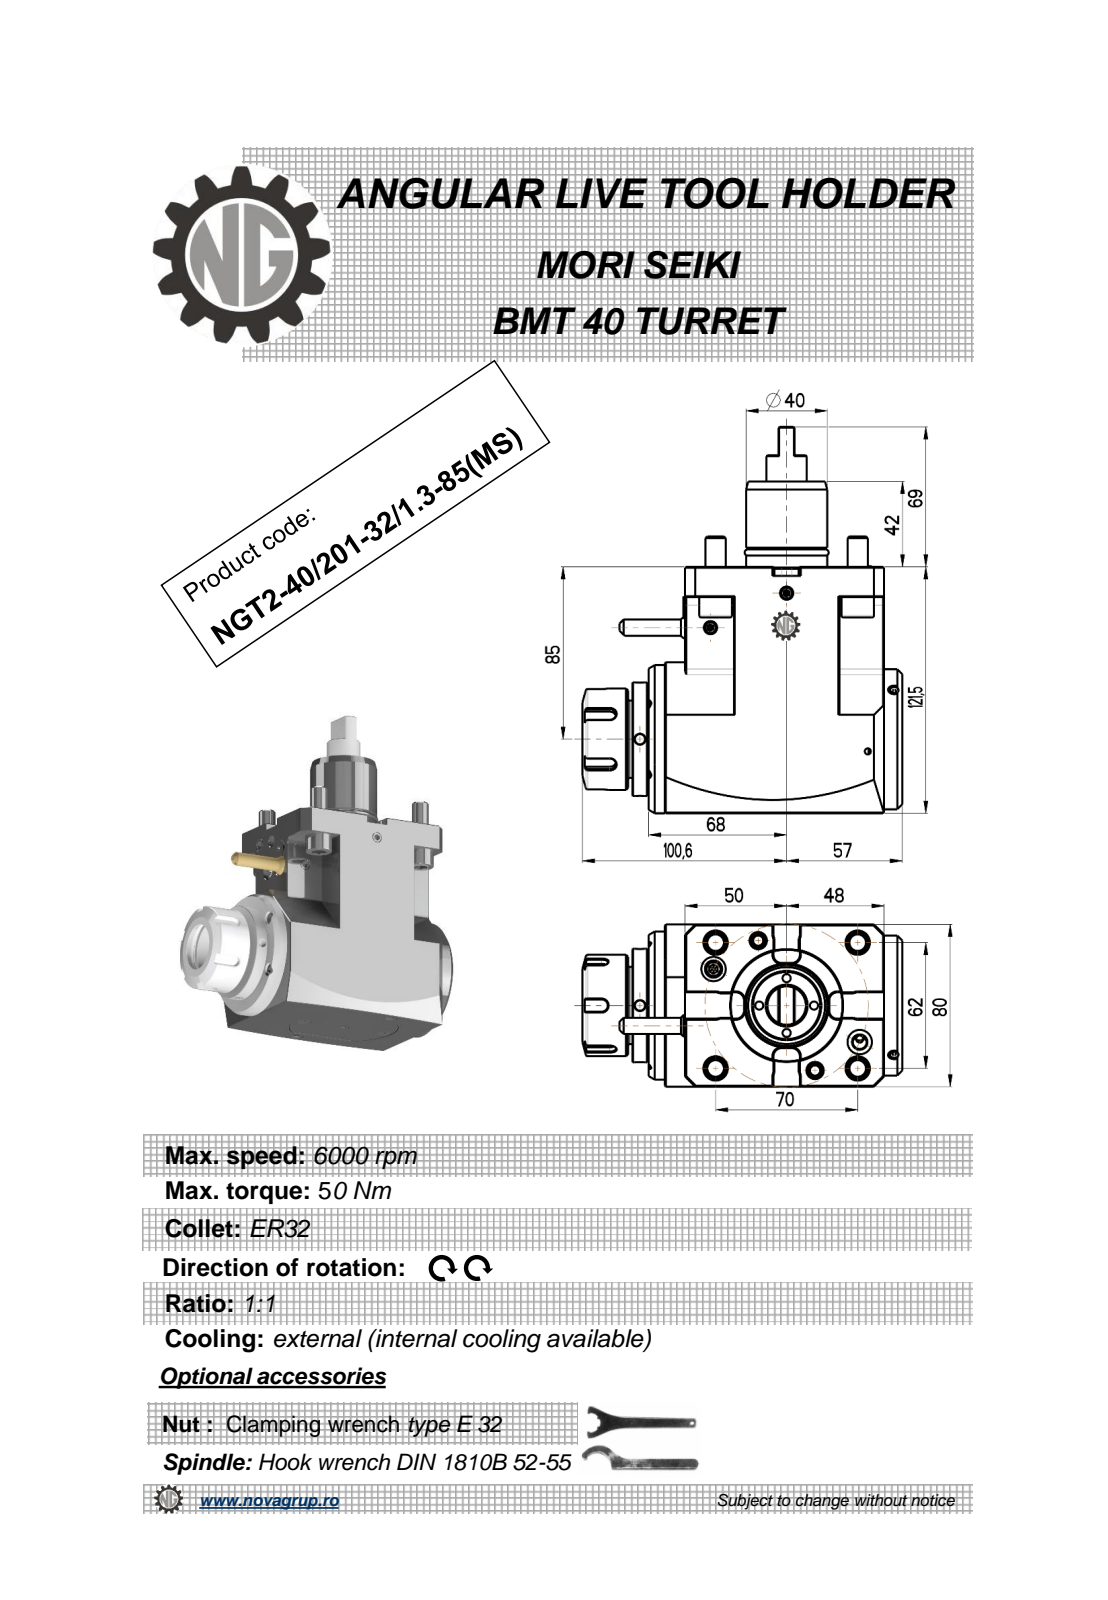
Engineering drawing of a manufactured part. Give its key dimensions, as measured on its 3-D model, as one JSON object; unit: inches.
{"part_name": "NGT2_40_201_32_1_3_85_MS", "step_written_by": "PRO/ENGINEER BY PARAMETRIC TECHNOLOGY CORPORATION, 2010280 (CONFIG_CONTROL_DESIGN)", "units": "inches", "bodies": {"solids": 2, "faces": 484, "planar": 179, "cylindrical": 105, "other": 200}, "overall_size": [7.5, 6.205, 3.213], "volume_in3": 66.45, "surface_area_in2": 145.2, "round_holes": [[0.197, 3], [0.268, 2], [0.118, 1], [1.063, 1]], "round_bosses_or_shafts": [[0.63, 4], [0.394, 4], [2.874, 1], [2.717, 1], [2.205, 1], [1.969, 1], [1.693, 1], [1.575, 1]], "partial_cylinders_radius": [[0.157, 20], [0.118, 5], [0.148, 4], [0.031, 2], [0.138, 2], [18.898, 2], [1.083, 1]], "face_to_face_distances": [3.15, 4.783, 0.354, 0.827, 1.654, 2.323, 0.709, 4.567, 0.315, 0.866], "hole_center_spacings": [1.593, 2.201, 3.169, 4.32]}
